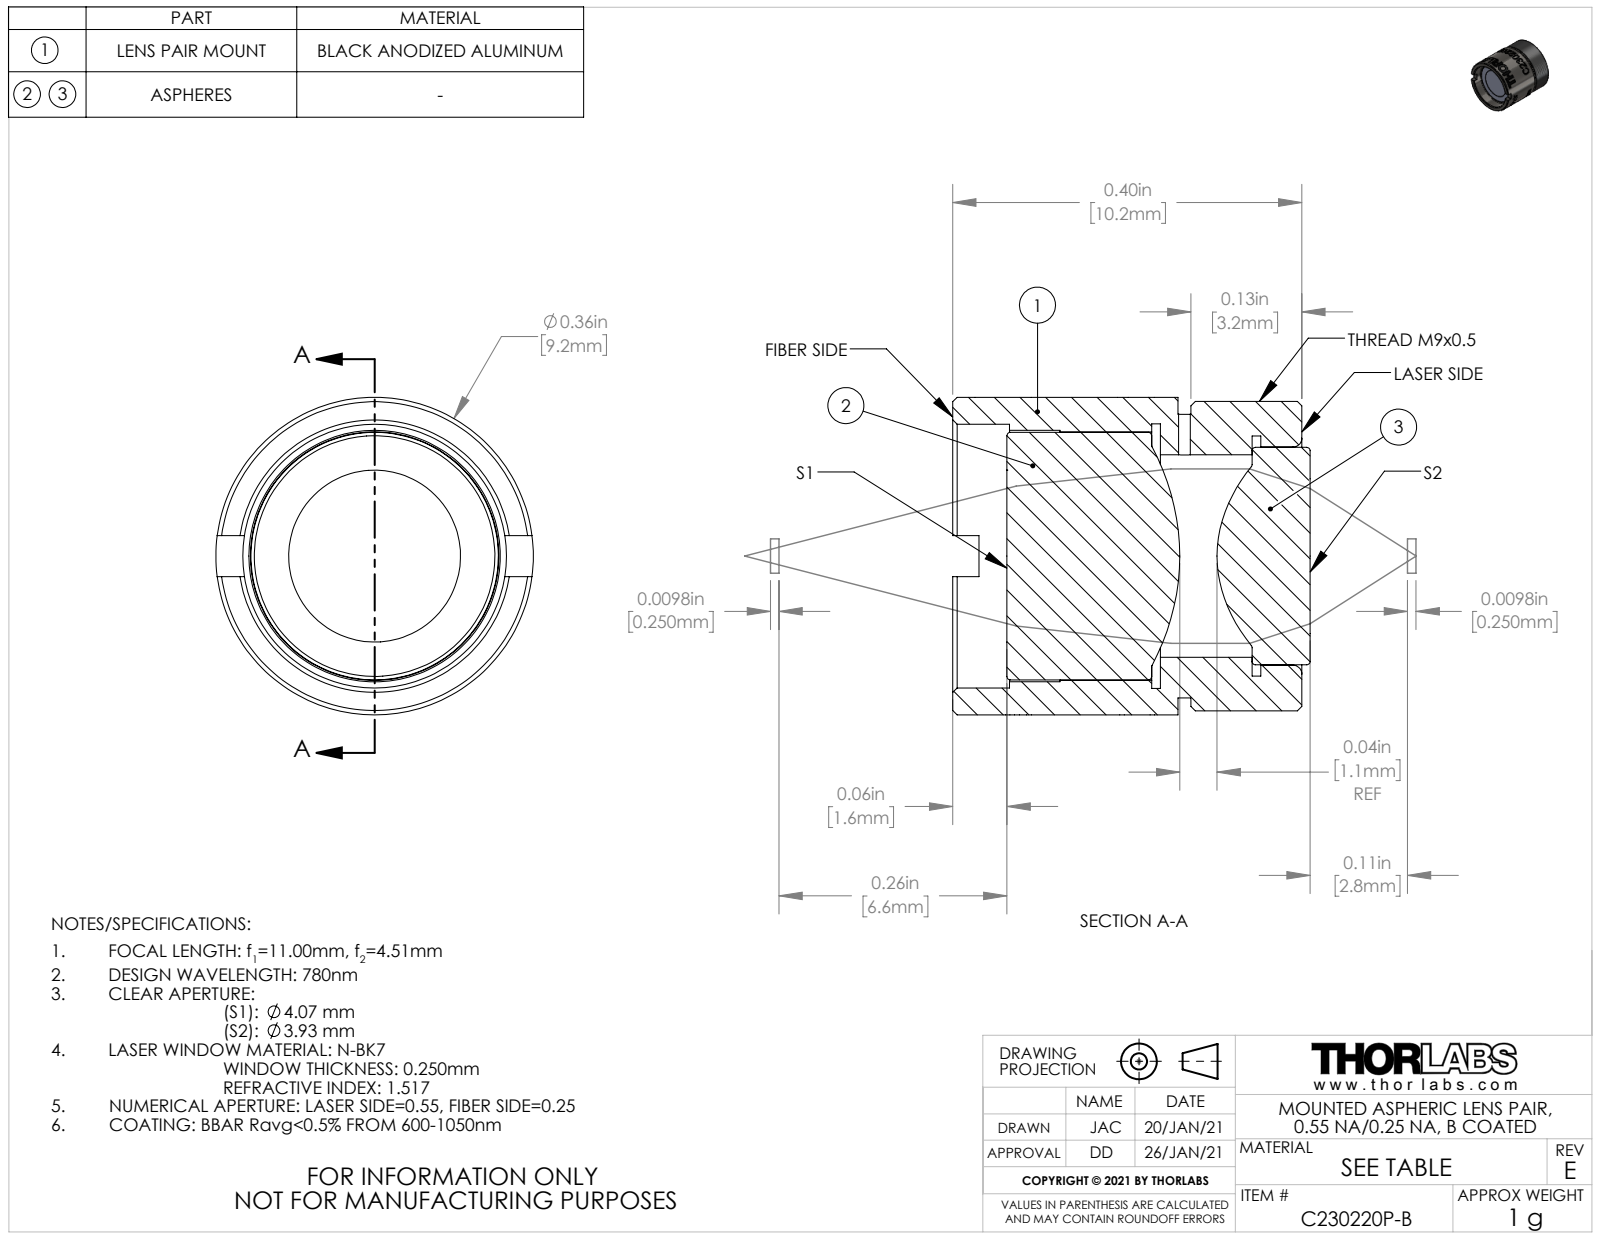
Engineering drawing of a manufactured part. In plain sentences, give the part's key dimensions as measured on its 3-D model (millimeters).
The part is named "0851-E0W". Its 3-D file was written by "SolidWorks 2018 (CONFIG_CONTROL_DESIGN)". It is 3 solids with 159 faces: 21 planar, 108 cylindrical and 30 other. Overall it measures 10.4 by 9.24 by 9.24 millimeters. Its volume is 531 cubic millimeters and its surface area 899 square millimeters. Round holes: 1 of diameter 0.34, 1 of diameter 5.89, 1 of diameter 6.35, 1 of diameter 6.99, 1 of diameter 7.23, 1 of diameter 7.32, 1 of diameter 7.67, 1 of diameter 7.7. Round bosses or shafts: 1 of diameter 9.24, 1 of diameter 9, 1 of diameter 8.26, 1 of diameter 7.2, 1 of diameter 6.33. The main face-to-face distances are 4.11, 8.58, 4.47, 1.45, 2.66, 7.13, 2.92, 1.69, 4.35, 8.82.
